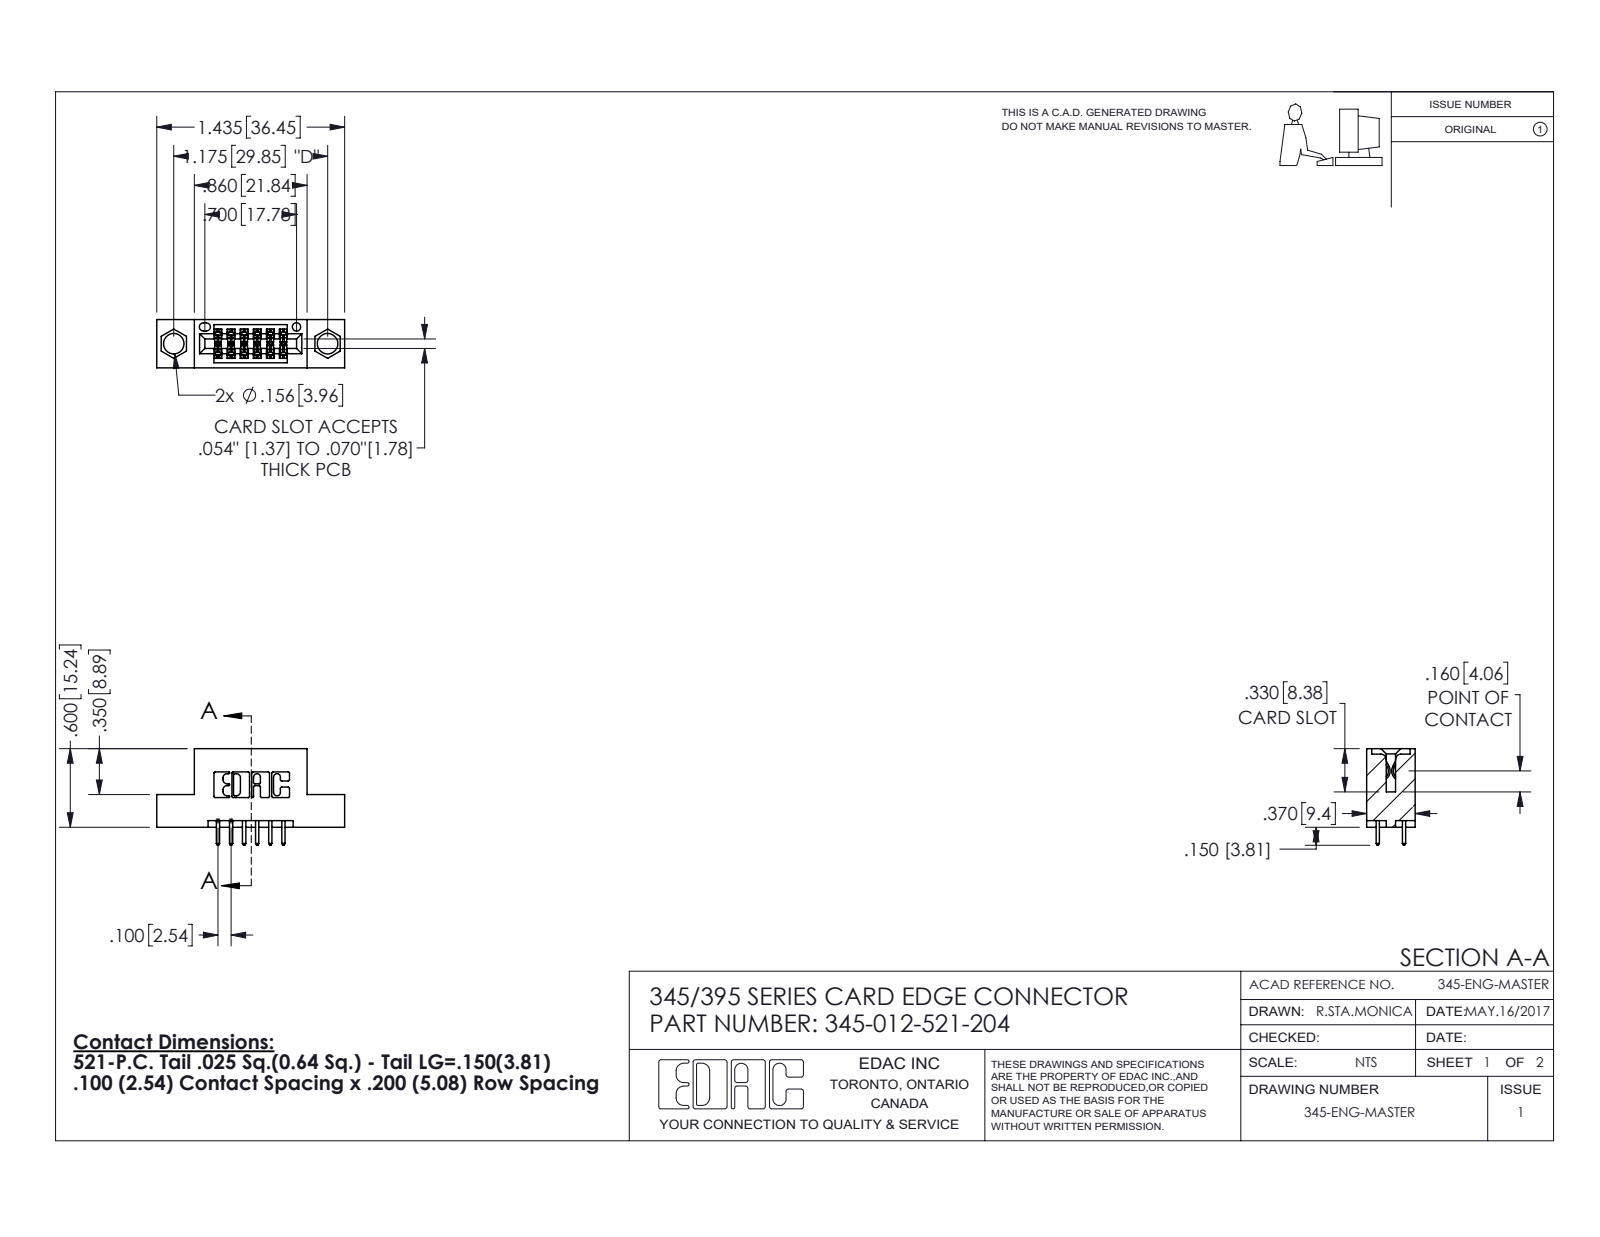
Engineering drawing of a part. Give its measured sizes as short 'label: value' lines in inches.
name: 345 Part_Flush Mounting Lugs - 0.156 Dia-TI; 345-012-521-204; 345-292-001_345-293-121
written by: SolidWorks 2020 (CONFIG_CONTROL_DESIGN)
unit: in
bodies: 13 solids, 740 faces (490 planar, 250 cylindrical, 0 other)
size: 1.435 × 0.737 × 0.37
volume: 0.189 in³; area: 5.733 in²
holes: 2× ⌀0.156, 1× ⌀0.064
rounds: 22× R0.01, 18× R0.006, 12× R0.01, 6× R0.007, 6× R0.031, 3× R0.026, 2× R0.014, 2× R0.019
face distances: 0.2, 0.37, 0.072, 0.298, 0.1, 0.098, 0.272, 0.025, 0.225, 0.06
hole spacings: 0.27, 0.946, 1.175
